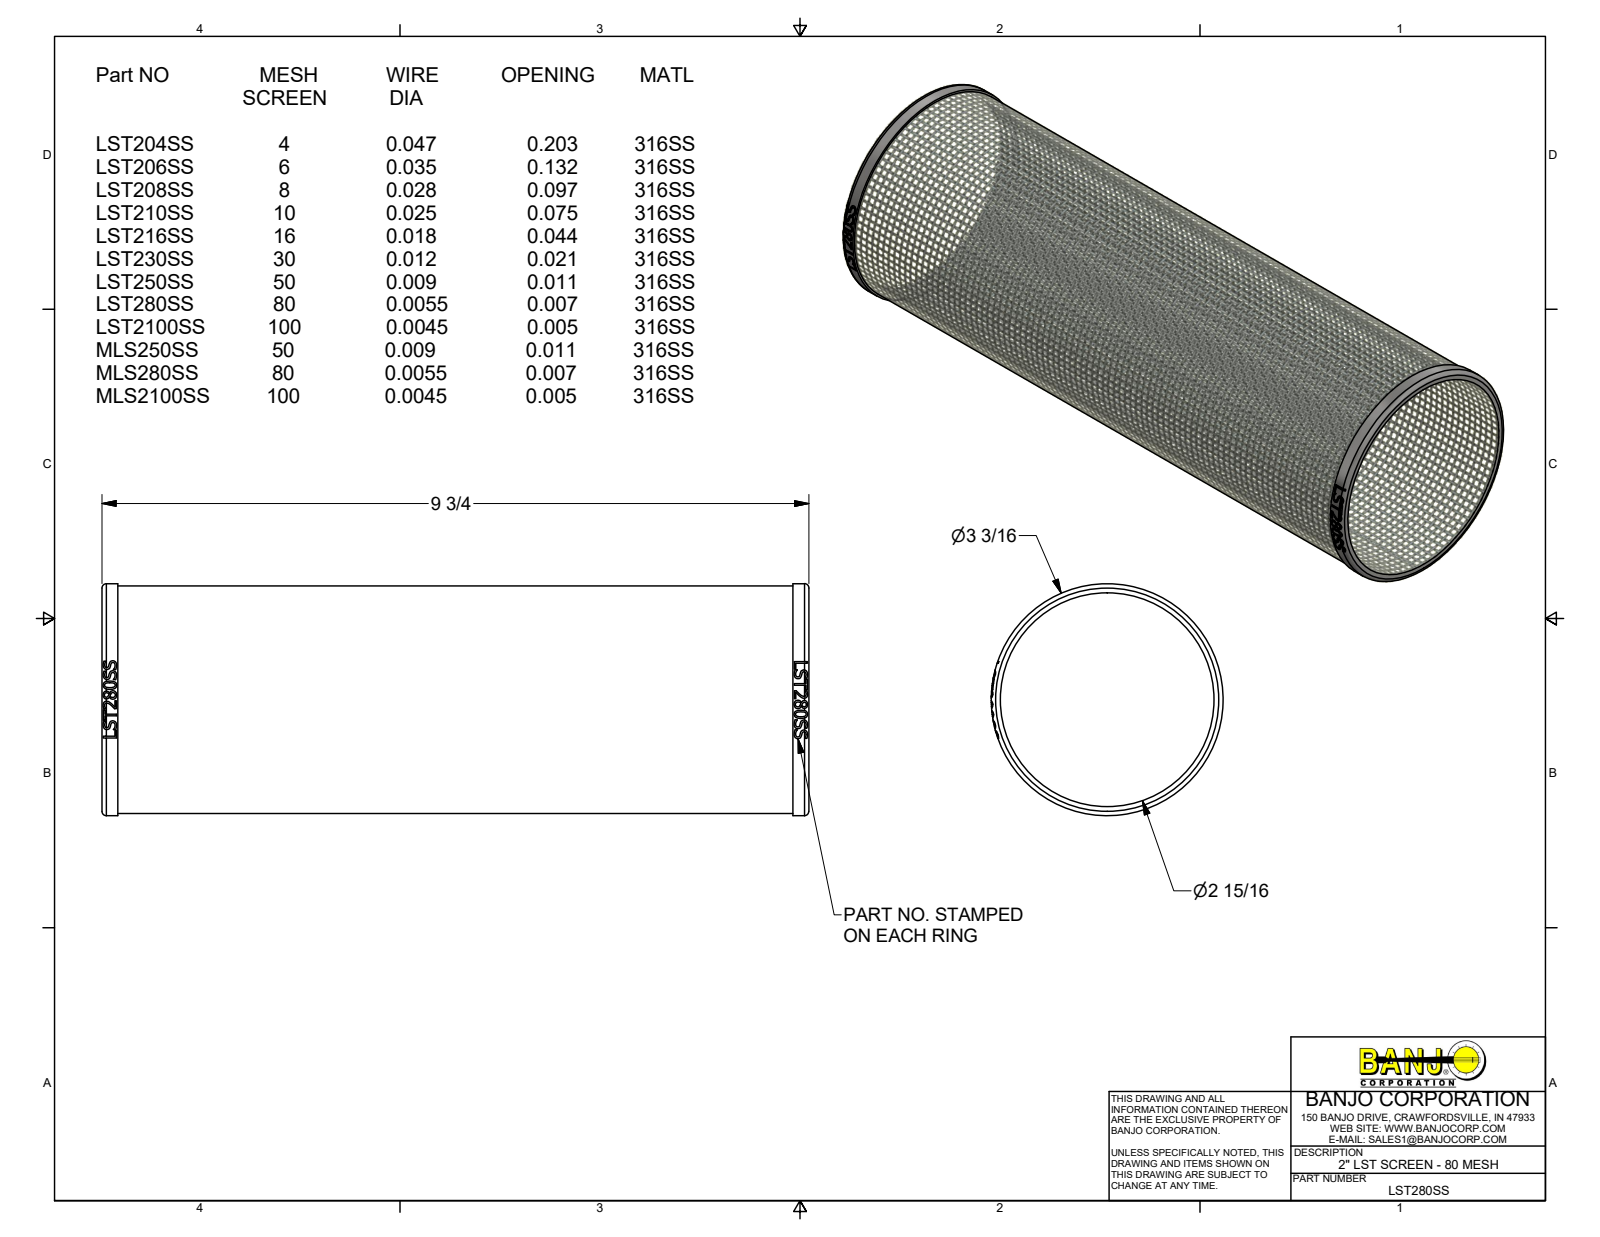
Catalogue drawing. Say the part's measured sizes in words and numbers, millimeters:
The part is named "LST280SS". Its 3-D file was written by "Autodesk Inventor 2017 (AUTOMOTIVE_DESIGN)". It is 1 solid with 280 faces: 72 planar, 26 cylindrical and 182 other. Overall it measures 246.89 by 80.97 by 80.97 millimeters. Its volume is 146 391 cubic millimeters and its surface area 121 299 square millimeters. Round holes: 1 of diameter 74.61. Round bosses or shafts: 1 of diameter 80.98, 1 of diameter 79.45. Partial cylindrical surfaces (rounded edges, fillets, slot ends): 1 of radius 39.98. The main face-to-face distances are 246.89, 241.33, 5.56, 235.77, 0.49, 7.69, 18.97, 8.3, 18.36, 0.61.
